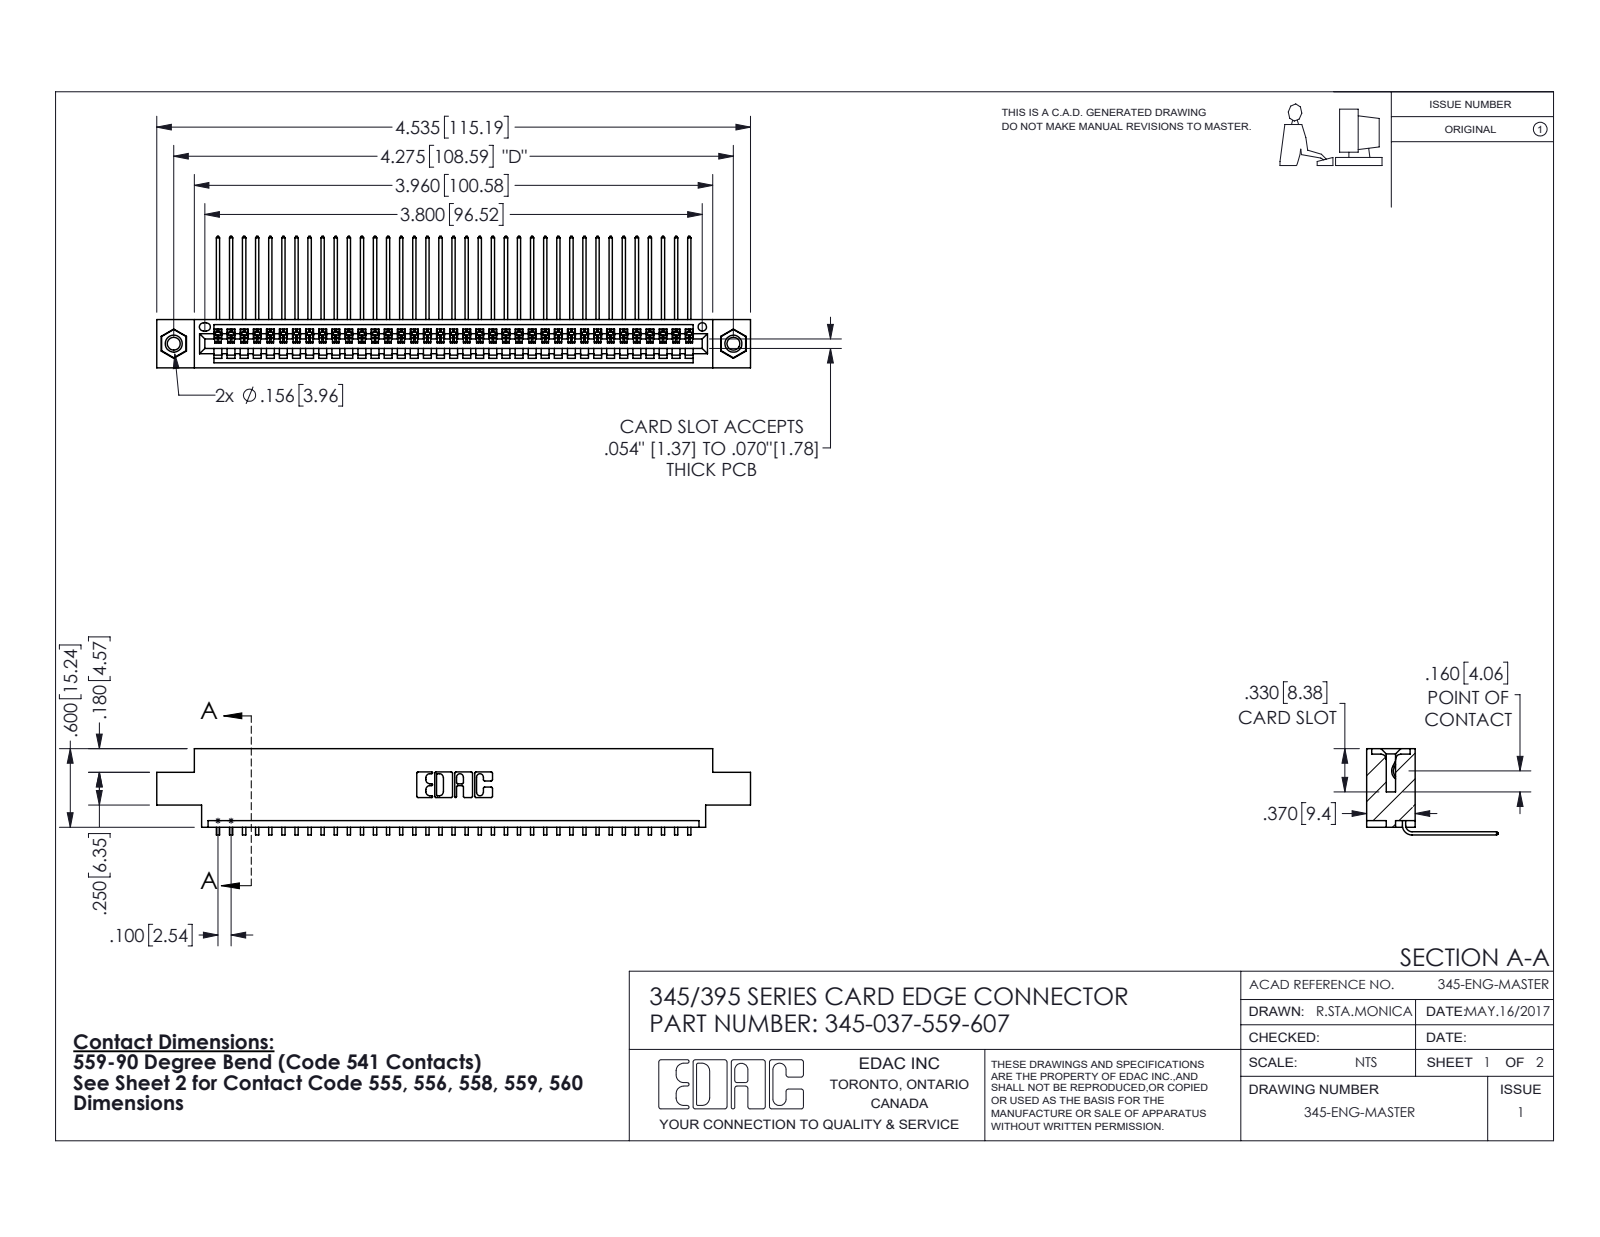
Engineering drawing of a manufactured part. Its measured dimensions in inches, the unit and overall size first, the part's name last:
Units: inches
Overall size (bounding box): 4.535 × 1.005 × 0.659
Round holes (diameter × count): ⌀0.098 ×2, ⌀0.125 ×2, ⌀0.156 ×2, ⌀0.064 ×1
Round bosses / shafts (diameter × count): ⌀0.155 ×2
Partial cylindrical surfaces — rounded edges, fillets, slot ends (radius × count): R0.006 ×74, R0.01 ×22, R0.007 ×6, R0.031 ×6, R0.026 ×3, R0.031 ×2, R0.04 ×2, R0.014 ×1
Main face-to-face distances: 0.072, 0.298, 0.37, 0.2, 0.098, 0.272, 0.025, 0.225, 0.175, 0.149
Hole centre spacings: 0.27, 4.039, 4.275
Volume: 0.665 in³ · Surface area: 23.71 in²
Bodies: 40 solids, 2410 faces (1670 planar, 724 cylindrical, 16 other)
Part name (STEP PRODUCT): 345 Part_0.170 Offset - 0.156 Dia-TI; 345-037-559-607; 345-250-001_345-250-005-103; 345-292-001_558 559 Tail - 1
STEP written by: SolidWorks 2016 (CONFIG_CONTROL_DESIGN)
